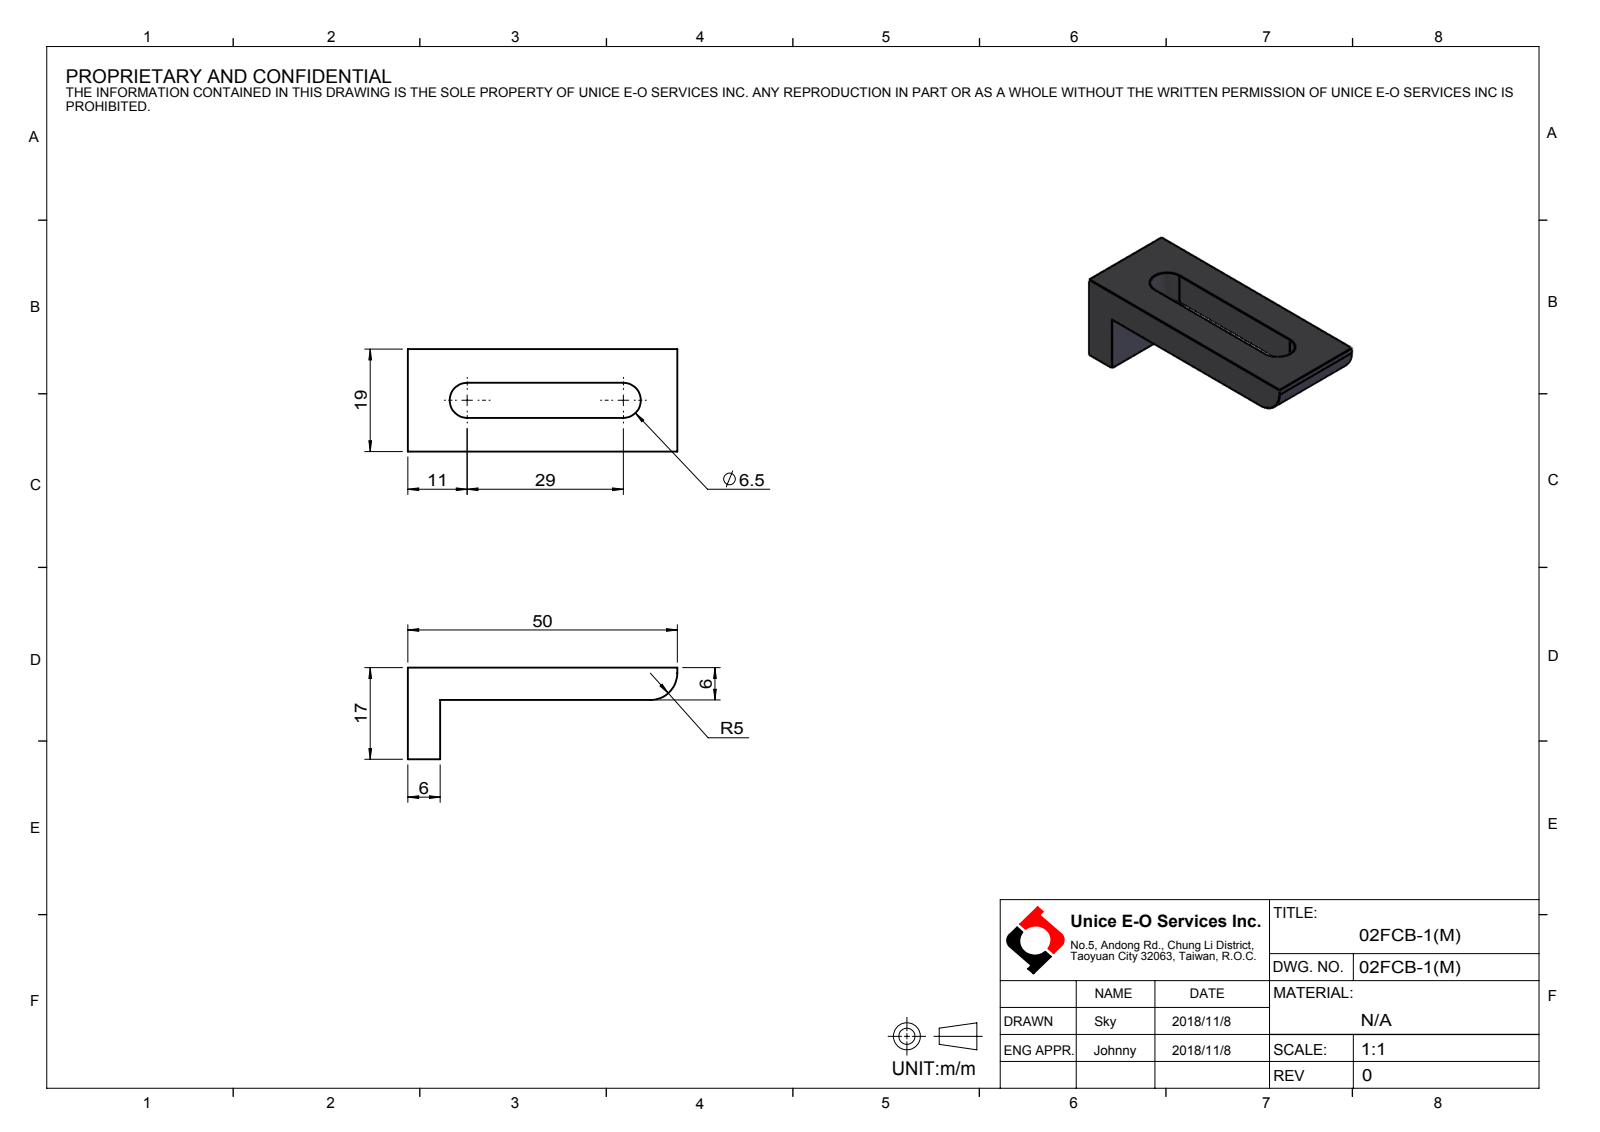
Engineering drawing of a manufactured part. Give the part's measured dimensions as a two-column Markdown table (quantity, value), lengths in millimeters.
| quantity | value |
| --- | --- |
| part name | 02FCB-1(M) |
| STEP written by | SolidWorks 2016 (AUTOMOTIVE_DESIGN) |
| units | millimeters |
| bodies | 1 solid, 14 faces (10 planar, 4 cylindrical, 0 other) |
| overall size | 50 × 19 × 17 |
| volume | 5 522 mm³ |
| surface area | 3 254 mm² |
| partial cylindrical surfaces (radius × count) | 3.25 × 2, 5 × 1 |
| main face-to-face distances | 6, 19, 6.25, 12.75, 6.5, 11, 17, 50, 44 |
